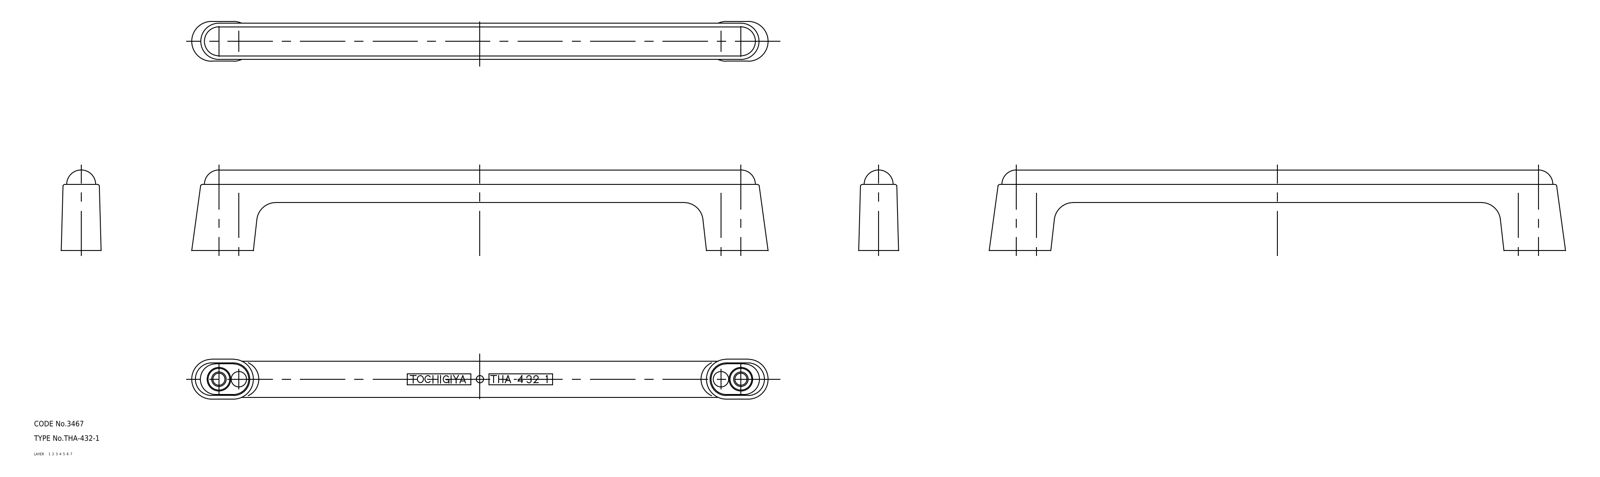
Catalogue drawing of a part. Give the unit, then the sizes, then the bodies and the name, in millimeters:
Units: millimetres
Overall size (bounding box): 318 × 44.5 × 22
Volume: 59 642 mm³ · Surface area: 51 521 mm²
Bodies: 2 solids, 127 faces (0 planar, 0 cylindrical, 127 other)
Part name (STEP PRODUCT): pull; cover; THA_432_1_140_36
STEP written by: CADfix (AUTOMOTIVE_DESIGN)
